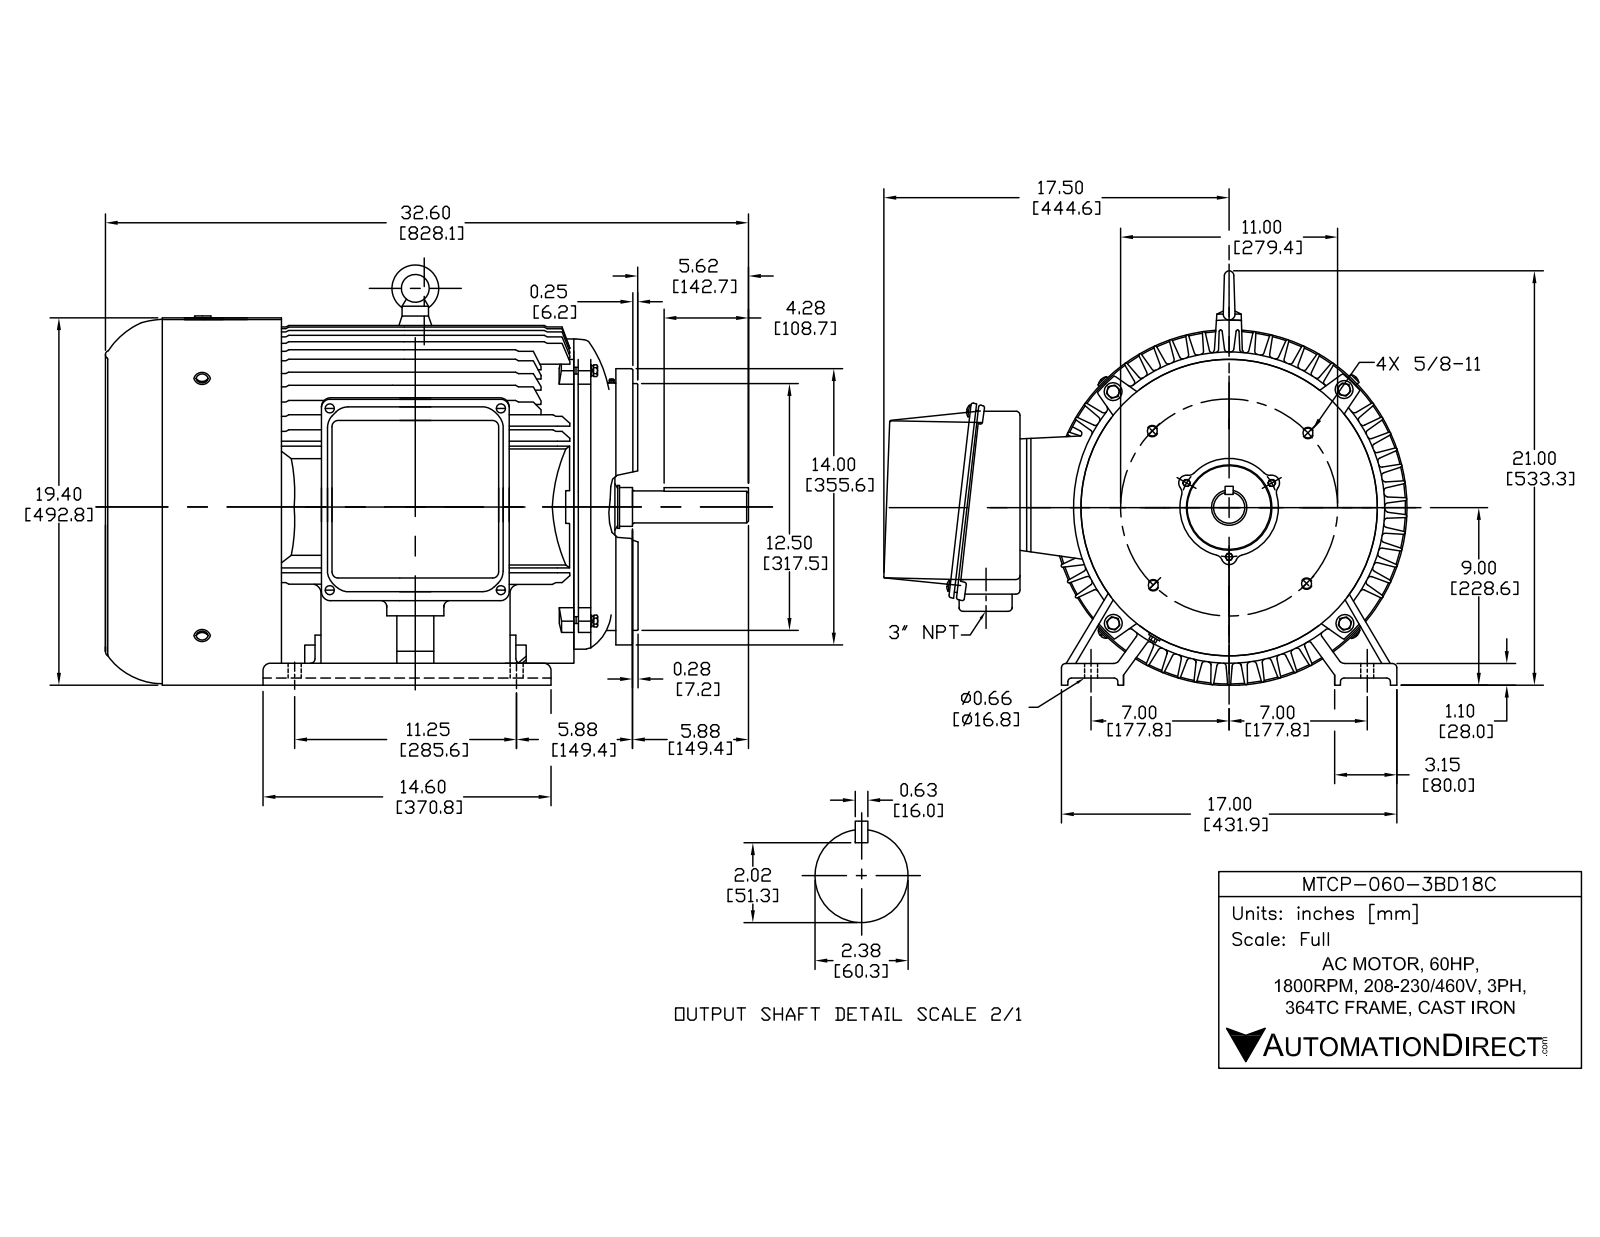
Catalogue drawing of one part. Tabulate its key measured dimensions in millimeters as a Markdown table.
| quantity | value |
| --- | --- |
| part name | spring lock washers--normal type gb_GB_FASTENER_WASHER_SW 6; PE360接线盒座_默认_按加工; hex head bolts-full thread grade c gb_GB_FASTENER_BOLT_HHBFTC M12X65-N; eyebolts gb_GB_FASTENER_SCREWS_FRS M16-N (+8 more) |
| STEP written by | SolidWorks 2017 (AUTOMOTIVE_DESIGN) |
| units | millimeters |
| bodies | 64 solids, 4172 faces (1021 planar, 1546 cylindrical, 1605 other) |
| overall size | 842.5 × 671.97 × 542.8 |
| volume | 20 020 000 mm³ |
| surface area | 4 868 000 mm² |
| round holes (diameter × count) | 10 × 19, 6.8 × 10, 13.49 × 10, 12 × 5, 5 × 4, 6 × 4, 6.4 × 4, 6.68 × 4, 10.2 × 4, 12.9 × 4, 13 × 4, 15 × 4 |
| round bosses / shafts (diameter × count) | 12 × 8, 8 × 8, 24 × 4, 19.1 × 4, 10 × 4, 9.88 × 4, 6 × 4, 481 × 1 |
| partial cylindrical surfaces (radius × count) | 1 × 196, 5 × 156, 2 × 121, 0.5 × 83, 1.5 × 40, 6 × 24, 12 × 20, 4 × 15 |
| main face-to-face distances | 6, 1.5, 25.5, 6.5, 226, 28.52, 2, 28, 5, 7 |
| hole center spacings | 130, 106.92, 139.7, 160.28, 258.13, 264.84, 338.52, 75 |
